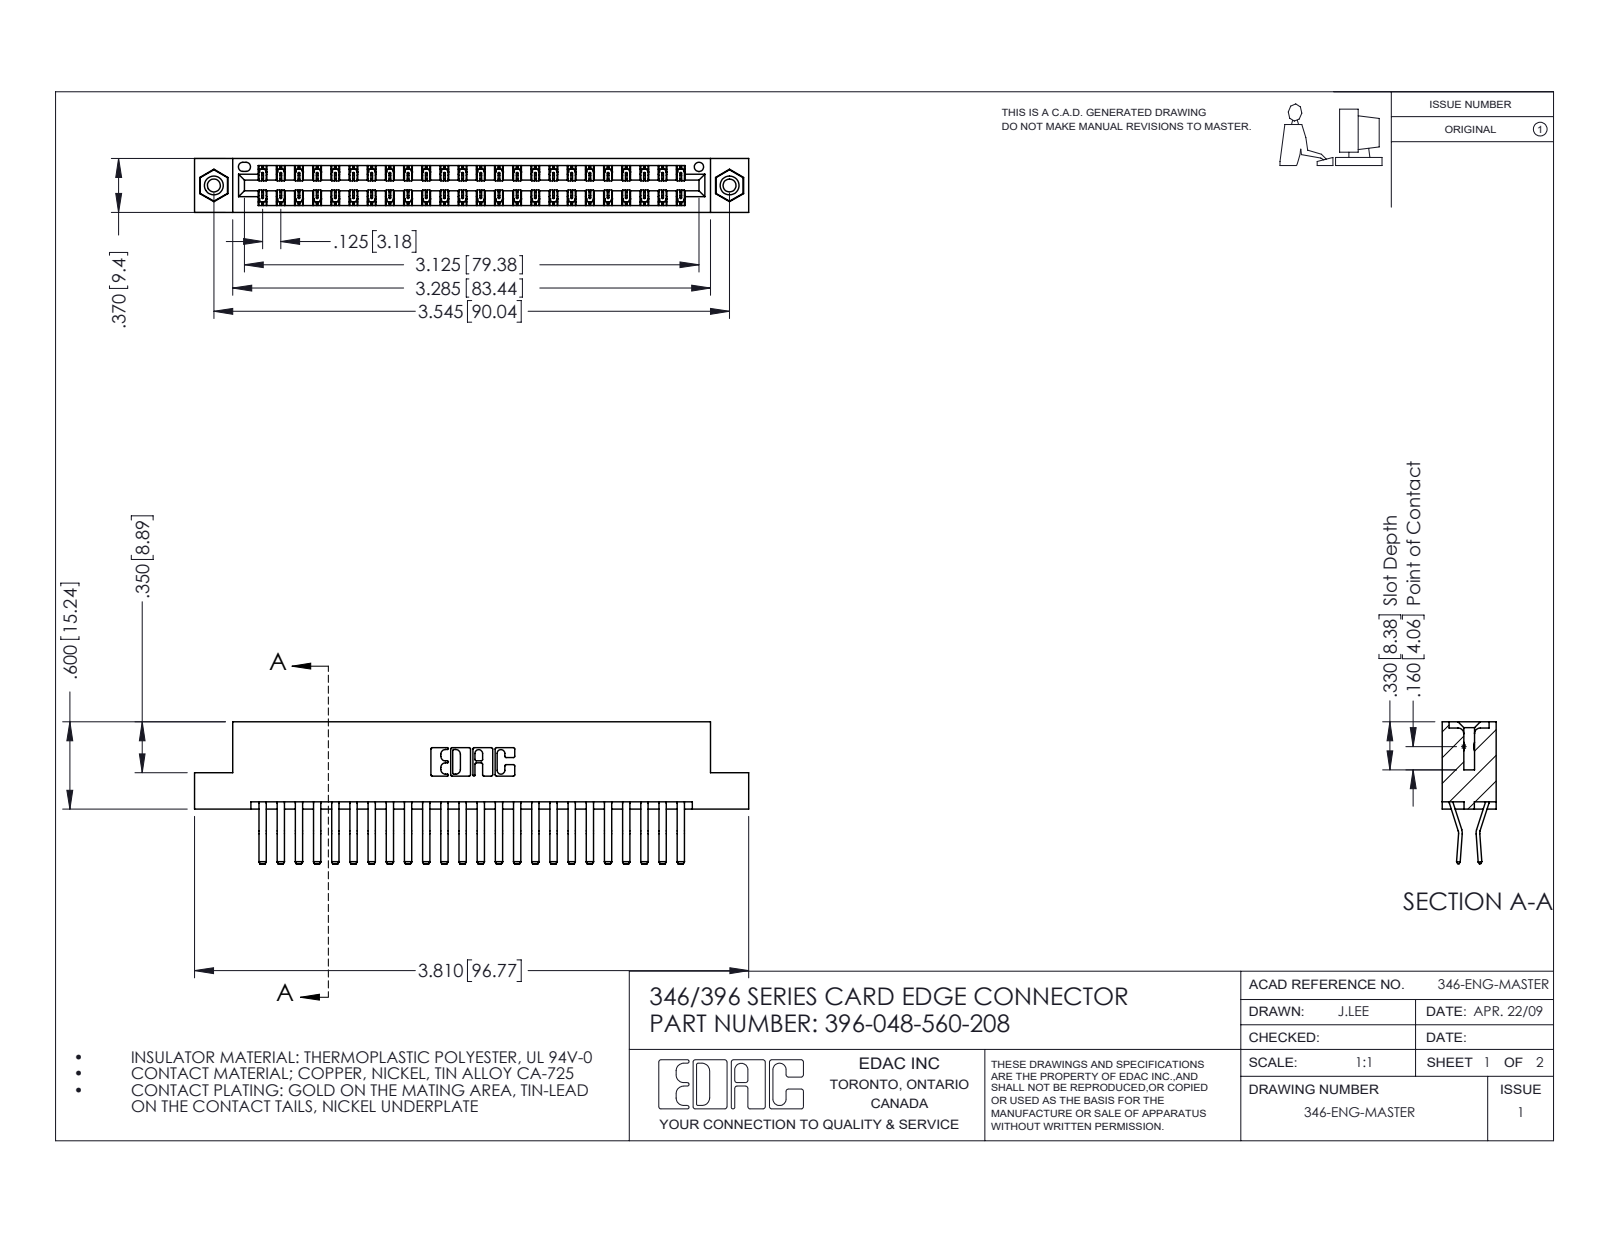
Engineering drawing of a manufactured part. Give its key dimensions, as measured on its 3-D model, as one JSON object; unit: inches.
{"part_name": "345-250-001_345-250-003-102; 346 Part_Flush Mounting Lugs - 0.156 Dia-TI; 345-292-001_560 Tail; 396-048-560-208", "step_written_by": "SolidWorks 2016 (CONFIG_CONTROL_DESIGN)", "units": "inches", "bodies": {"solids": 51, "faces": 2774, "planar": 1788, "cylindrical": 970, "other": 16}, "overall_size": [3.81, 0.975, 0.37], "volume_in3": 0.586, "surface_area_in2": 21.36, "round_holes": [[0.089, 2], [0.125, 2], [0.156, 2], [0.064, 1]], "round_bosses_or_shafts": [[0.155, 2]], "partial_cylinders_radius": [[0.006, 72], [0.01, 22], [0.007, 6], [0.031, 6], [0.026, 3], [0.01, 2], [0.014, 2], [0.022, 2]], "face_to_face_distances": [0.048, 0.322, 0.37, 0.25, 0.025, 0.072, 0.298, 0.275, 0.148, 0.222], "hole_center_spacings": [0.246, 3.337, 3.545]}
